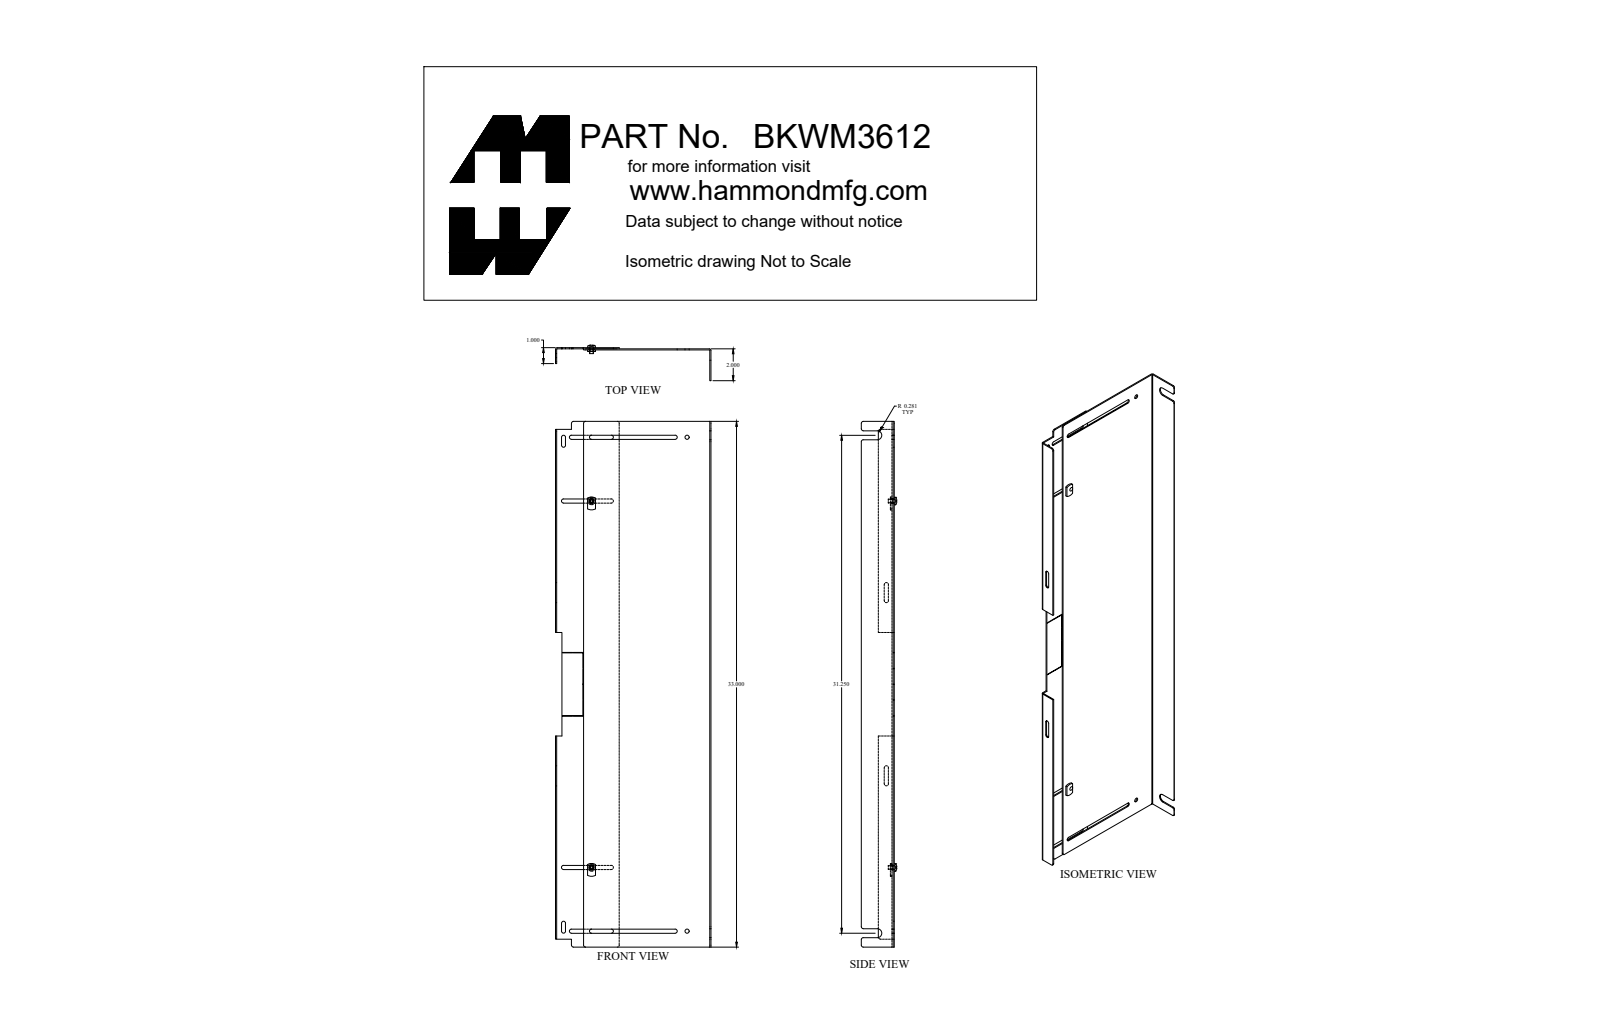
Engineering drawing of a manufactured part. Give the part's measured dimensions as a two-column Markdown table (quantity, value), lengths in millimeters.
| quantity | value |
| --- | --- |
| part name | BKWM3612_Default |
| STEP written by | SolidWorks 2019 (CONFIG_CONTROL_DESIGN) |
| units | millimeters |
| bodies | 6 solids, 216 faces (116 planar, 78 cylindrical, 22 other) |
| overall size | 838.2 × 247.9 × 56.8 |
| volume | 556 000 mm³ |
| surface area | 619 000 mm² |
| round holes (diameter × count) | 5.1 × 2, 6.6 × 2, 8 × 2 |
| round bosses / shafts (diameter × count) | 11.9 × 2, 7.4 × 2, 6.4 × 2 |
| partial cylindrical surfaces (radius × count) | 3.2 × 18, 3.3 × 16, 12.7 × 4, 0.9 × 2, 2.7 × 2, 7.1 × 2 |
| main face-to-face distances | 1.8, 3.7, 246.1, 244.3, 247.9, 101.6, 44.7, 42.9, 201.4, 203.2 |
| hole center spacings | 183.2, 702.5, 584.2, 787.4 |
